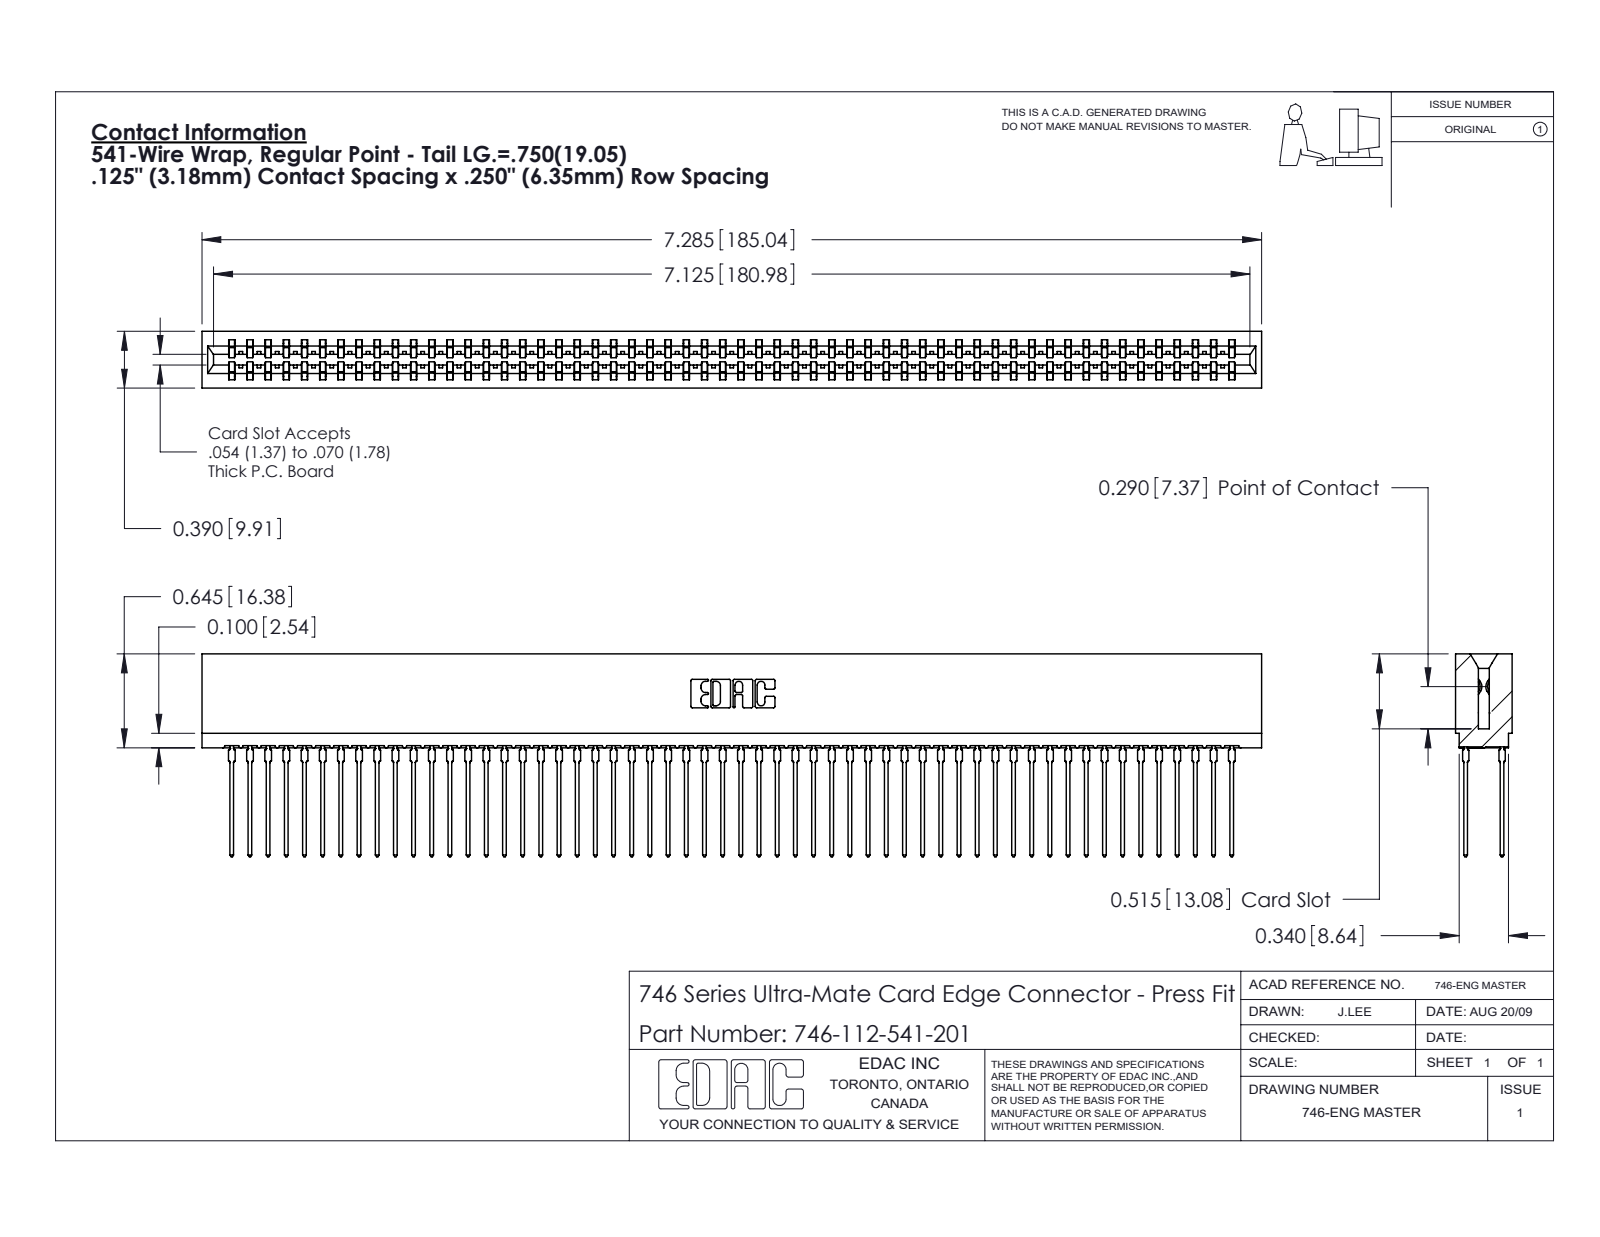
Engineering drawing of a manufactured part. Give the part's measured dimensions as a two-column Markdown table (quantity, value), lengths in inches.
| quantity | value |
| --- | --- |
| part name | 746 Part_.515 Slot Depth - 01; 746-112-541-201; 746-292-001_541 |
| STEP written by | SolidWorks 2020 (CONFIG_CONTROL_DESIGN) |
| units | inches |
| bodies | 113 solids, 10121 faces (5207 planar, 2002 cylindrical, 2912 other) |
| overall size | 7.285 × 1.394 × 0.39 |
| volume | 1.242 in³ |
| surface area | 55.56 in² |
| partial cylindrical surfaces (radius × count) | 0.021 × 224, 0.015 × 57, 0.01 × 22, 0.005 × 8, 0.011 × 8, 0.007 × 6, 0.031 × 6, 0.026 × 3 |
| main face-to-face distances | 0.057, 0.333, 0.25, 0.025, 0.307, 0.39, 0.083, 0.275, 0.174, 0.158 |
